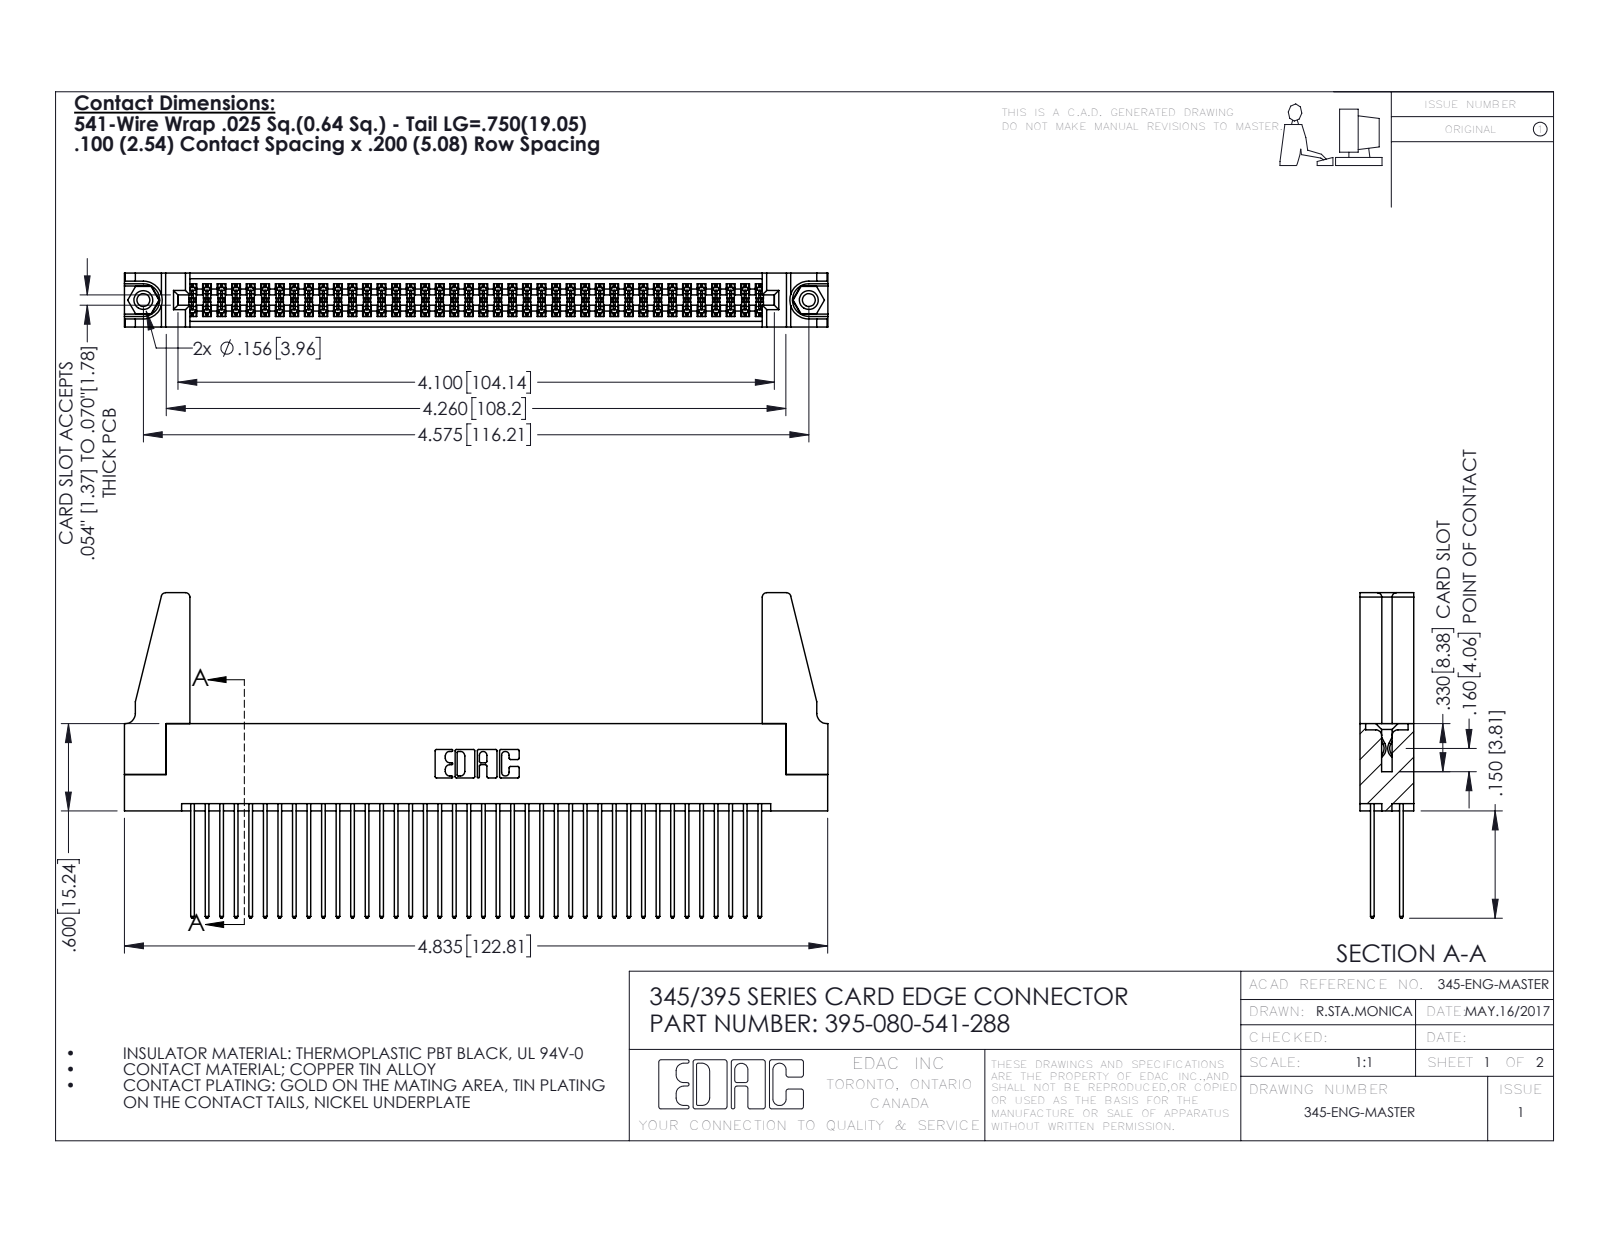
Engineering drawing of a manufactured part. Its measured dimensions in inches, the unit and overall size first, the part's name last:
Units: inches
Overall size (bounding box): 4.836 × 2.237 × 0.37
Round holes (diameter × count): ⌀0.089 ×2, ⌀0.125 ×2, ⌀0.156 ×2, ⌀0.064 ×1
Round bosses / shafts (diameter × count): ⌀0.155 ×2
Partial cylindrical surfaces — rounded edges, fillets, slot ends (radius × count): R0.006 ×120, R0.01 ×80, R0.01 ×22, R0.03 ×8, R0.007 ×6, R0.031 ×6, R0.026 ×3, R0.014 ×2
Main face-to-face distances: 0.072, 0.298, 0.2, 0.098, 0.272, 0.025, 0.37, 0.225, 0.175, 0.149
Hole centre spacings: 0.27, 4.339, 4.575
Volume: 0.954 in³ · Surface area: 36.47 in²
Bodies: 85 solids, 4250 faces (2792 planar, 1442 cylindrical, 16 other)
Part name (STEP PRODUCT): 345-250-001_345-250-001-102; 395-080-541-288; 345 Part_Flush Mounting Lugs - 0.156 Dia-TH; 345-292-001_345-293-141 (+1 more)
STEP written by: SolidWorks 2016 (CONFIG_CONTROL_DESIGN)
